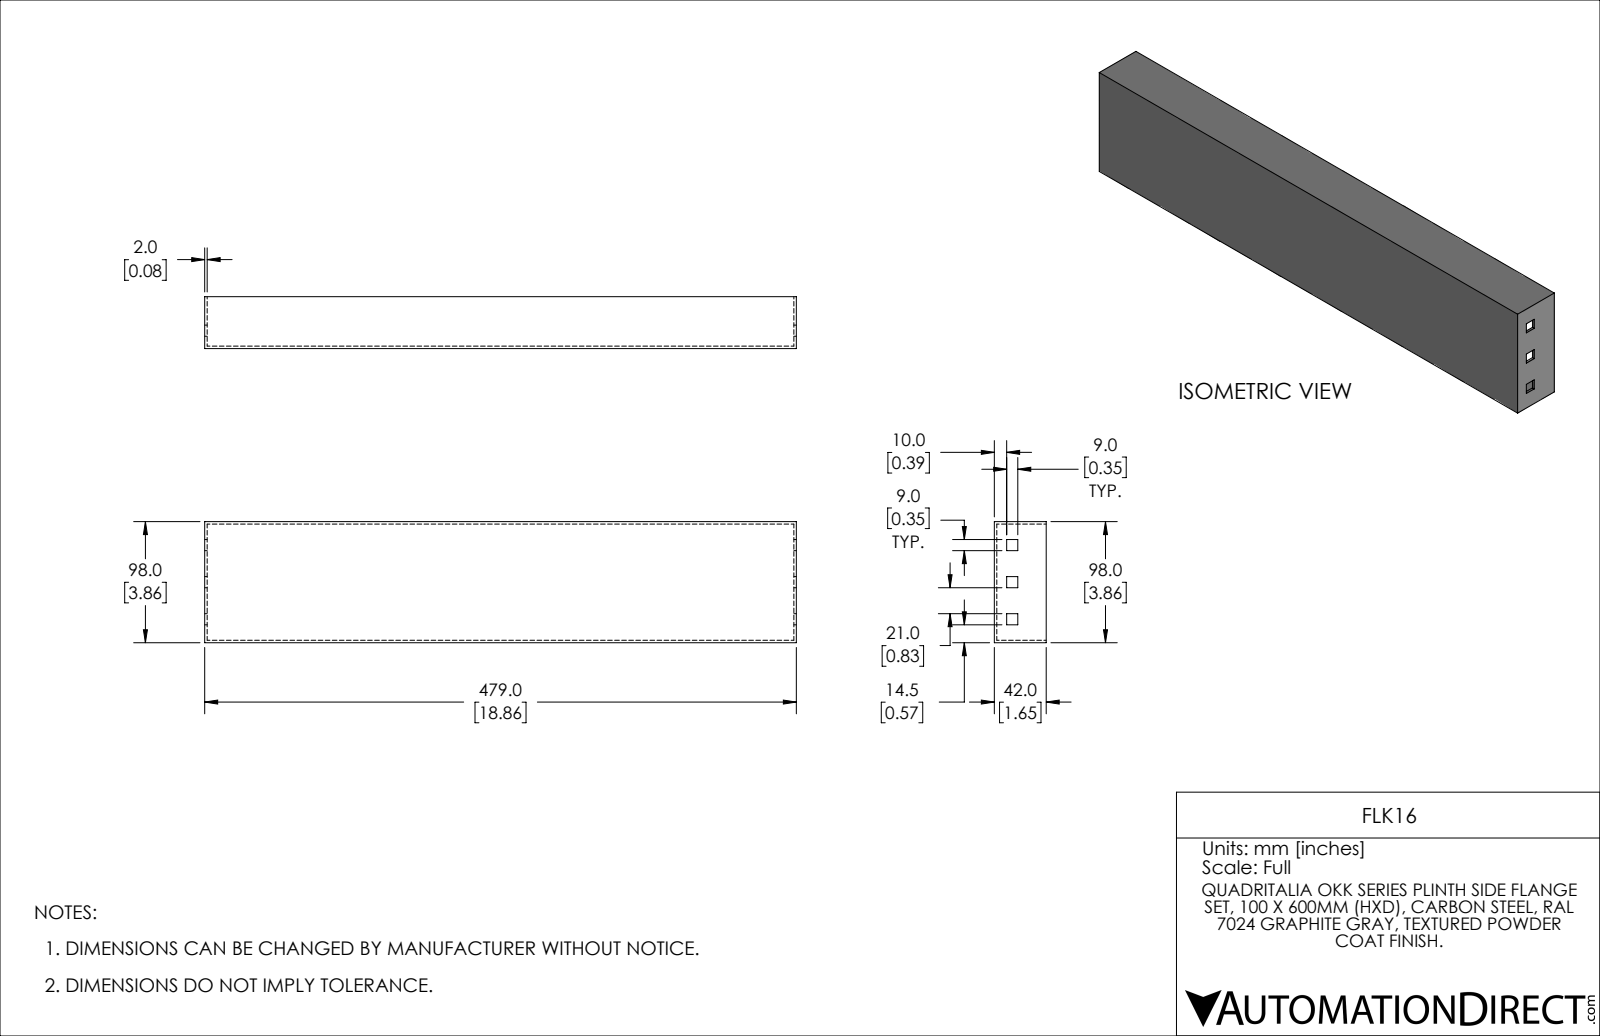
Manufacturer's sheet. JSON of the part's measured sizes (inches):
{"part_name": "FLK16", "step_written_by": "SolidWorks 2021 (CONFIG_CONTROL_DESIGN)", "units": "inches", "bodies": {"solids": 1, "faces": 35, "planar": 35, "cylindrical": 0, "other": 0}, "overall_size": [18.858, 3.858, 1.654], "volume_in3": 11.26, "surface_area_in2": 290.4, "face_to_face_distances": [0.079, 3.78, 3.858, 3.701, 18.78, 18.858, 18.701, 1.654, 1.575, 0.354]}
